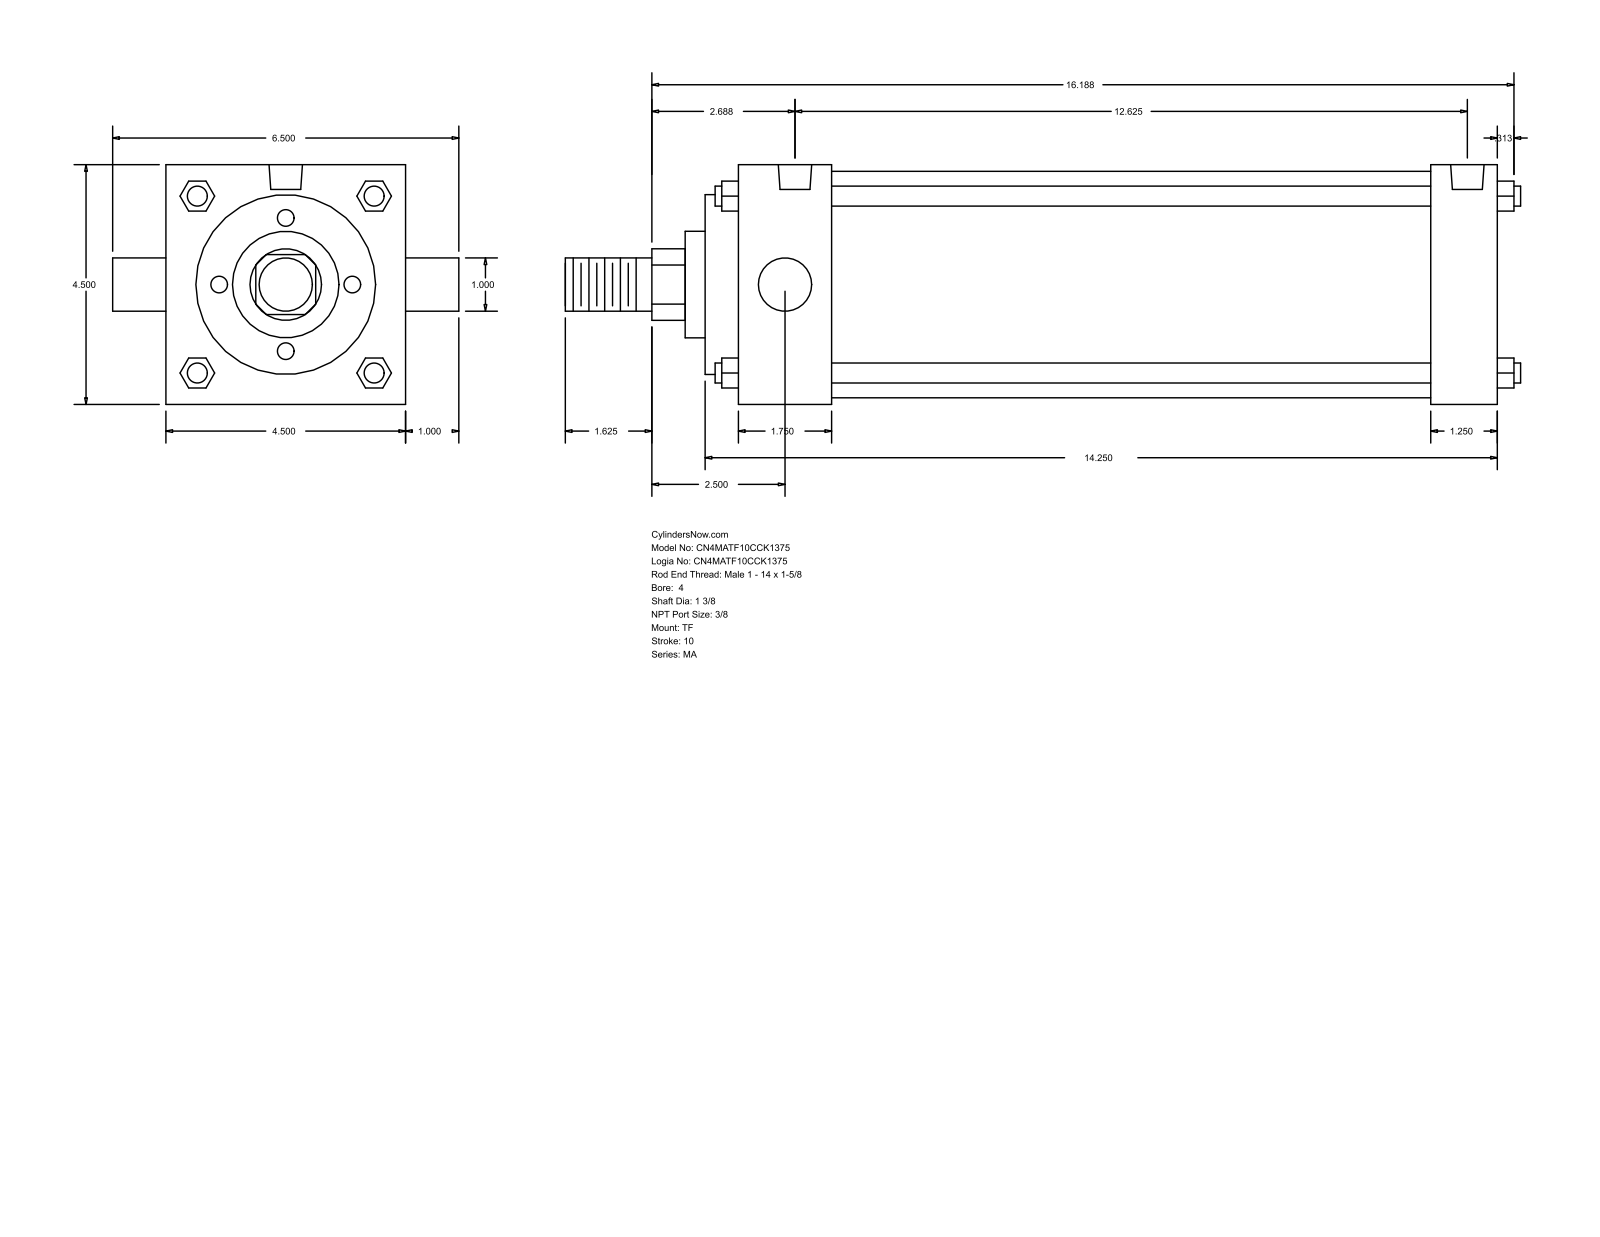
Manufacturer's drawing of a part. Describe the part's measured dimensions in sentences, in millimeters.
The part is named "MA_TF__0400_1.375". Its 3-D file was written by "GSSL Pune (CONFIG_CONTROL_DESIGN)". It is 0 solids with 122 faces: 93 planar, 29 cylindrical and 0 other. Overall it measures 455.61 by 165.1 by 114.3 millimeters. Round holes: 3 of diameter 11.11, 2 of diameter 15.93. Round bosses or shafts: 4 of diameter 9.53, 2 of diameter 25.4, 1 of diameter 107.95, 1 of diameter 85.72, 1 of diameter 50.8, 1 of diameter 34.92. Partial cylindrical surfaces (rounded edges, fillets, slot ends): 1 of radius 17.06. The main face-to-face distances are 114.3, 361.96, 15.87, 377.83, 346.08, 330.21, 31.75, 60.32, 44.45, 285.76. The hole center spacings are 4.76, 4.77, 311.15, 315.91, 315.92, 320.68.
